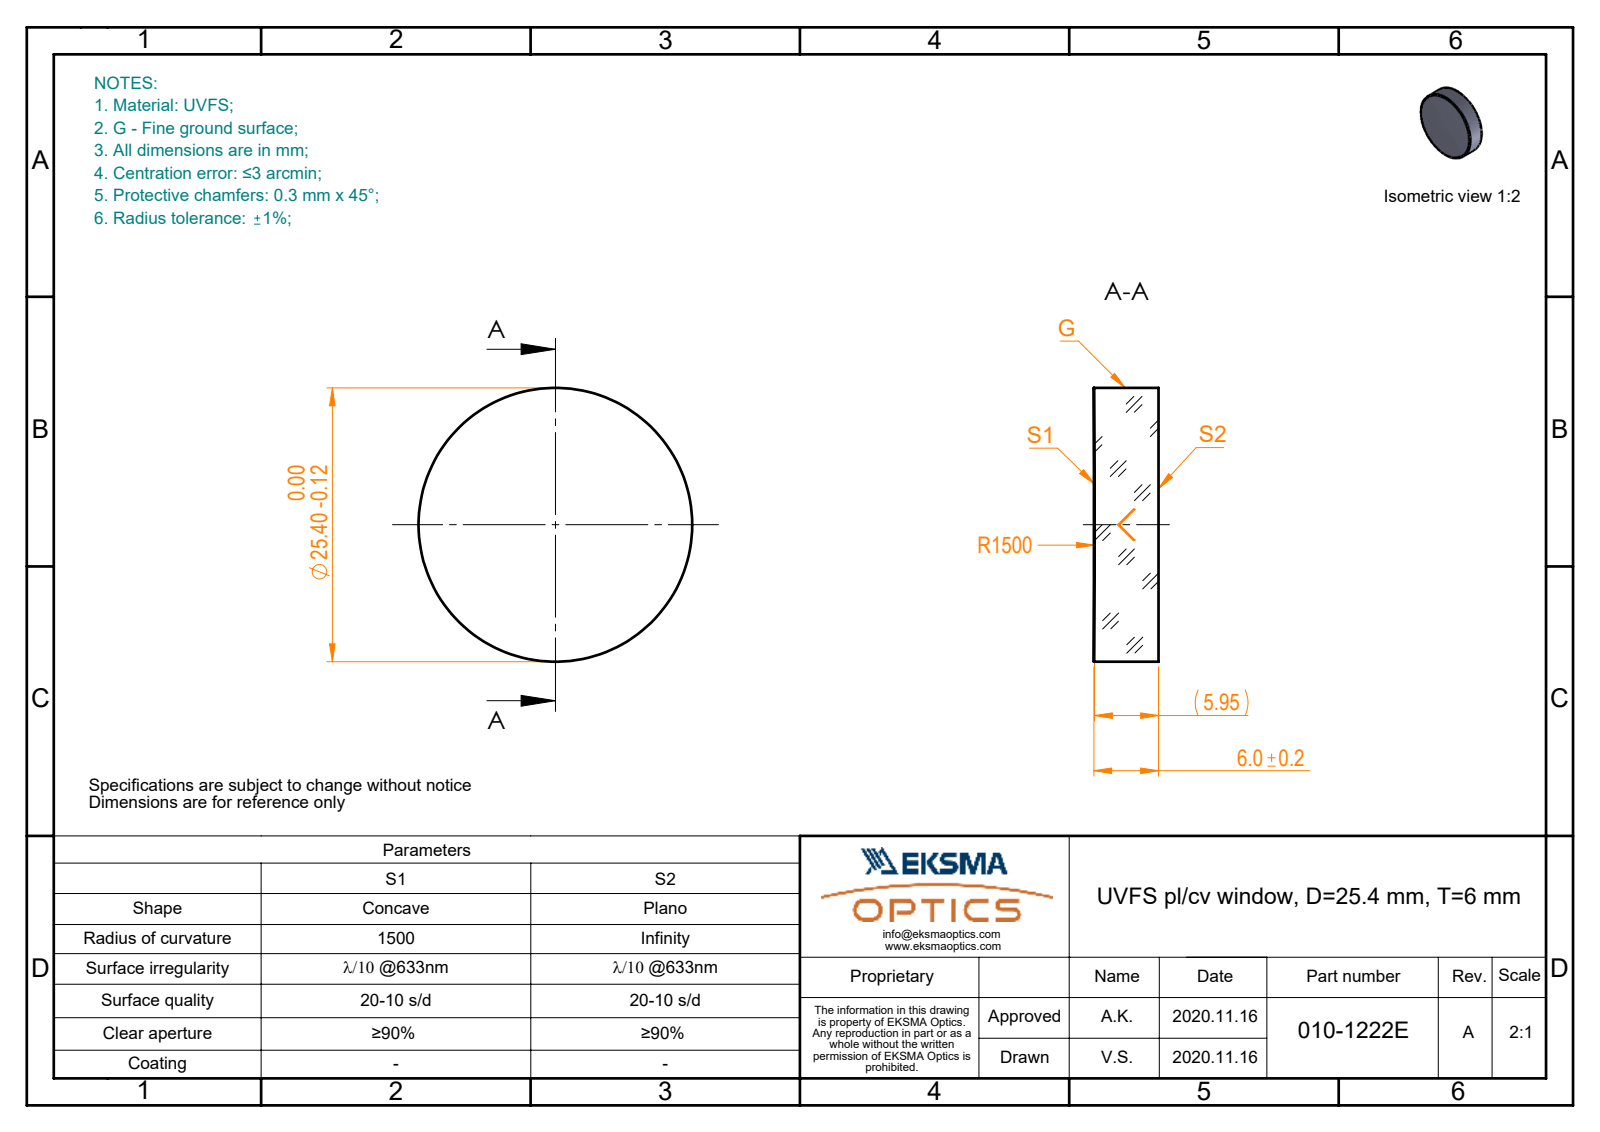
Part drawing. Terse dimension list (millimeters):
name: 010-1222E_UVFS_PCV_window
written by: SolidWorks 2019 (CONFIG_CONTROL_DESIGN)
unit: mm
bodies: 1 solid, 5 faces (1 planar, 2 cylindrical, 2 other)
size: 25.4 × 25.4 × 6
volume: 3 027 mm³; area: 1 492 mm²
bosses: 1× ⌀25.4
